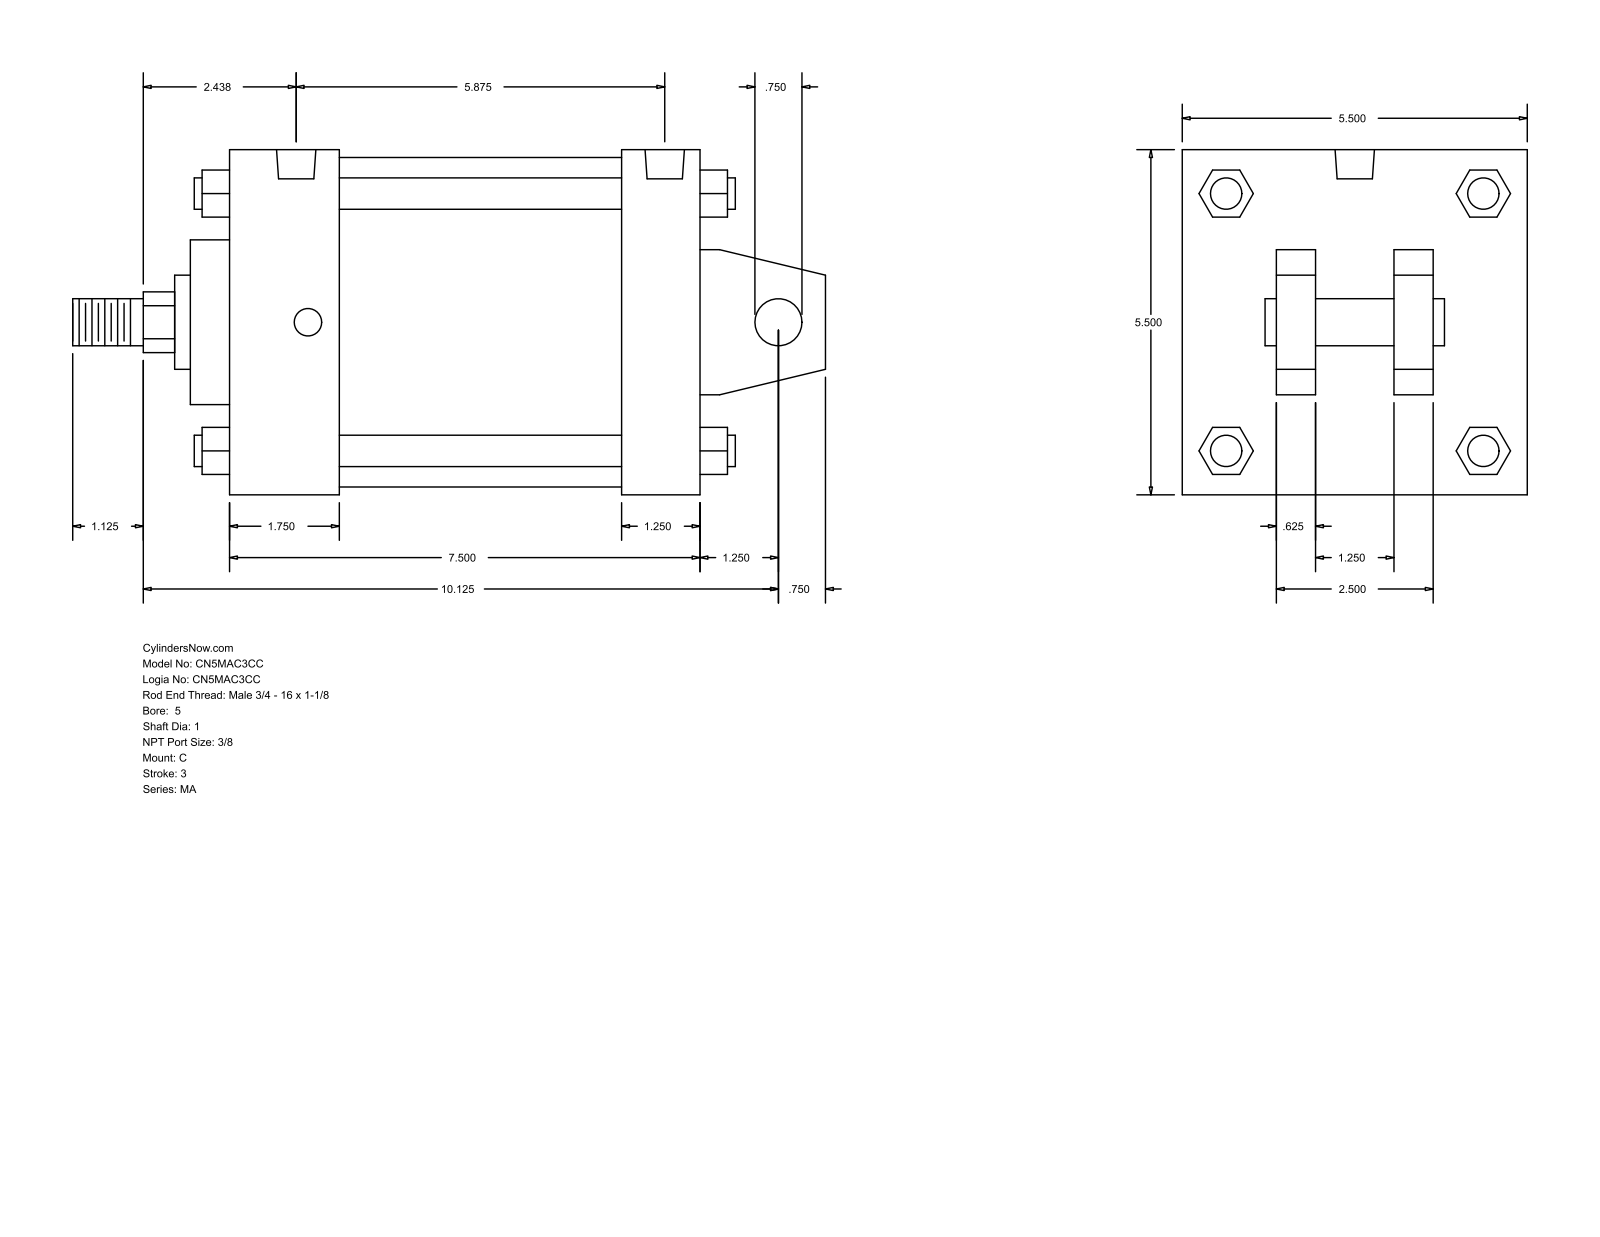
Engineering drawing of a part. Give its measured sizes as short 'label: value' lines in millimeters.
name: MA_C__0500_1
written by: GSSL Pune (CONFIG_CONTROL_DESIGN)
unit: mm
bodies: 0 solids, 141 faces (109 planar, 32 cylindrical, 0 other)
size: 304.8 × 139.7 × 139.7
holes: 4× ⌀11.11, 2× ⌀15.93
bosses: 4× ⌀12.7, 2× ⌀19.05, 1× ⌀133.35, 1× ⌀66.67, 1× ⌀38.1, 1× ⌀25.4
rounds: 1× R12.29
face distances: 139.7, 190.51, 15.87, 158.76, 31.75, 44.46, 114.3, 146.05, 38.1, 101.6
hole spacings: 4.76, 139.71, 144.47, 149.23
